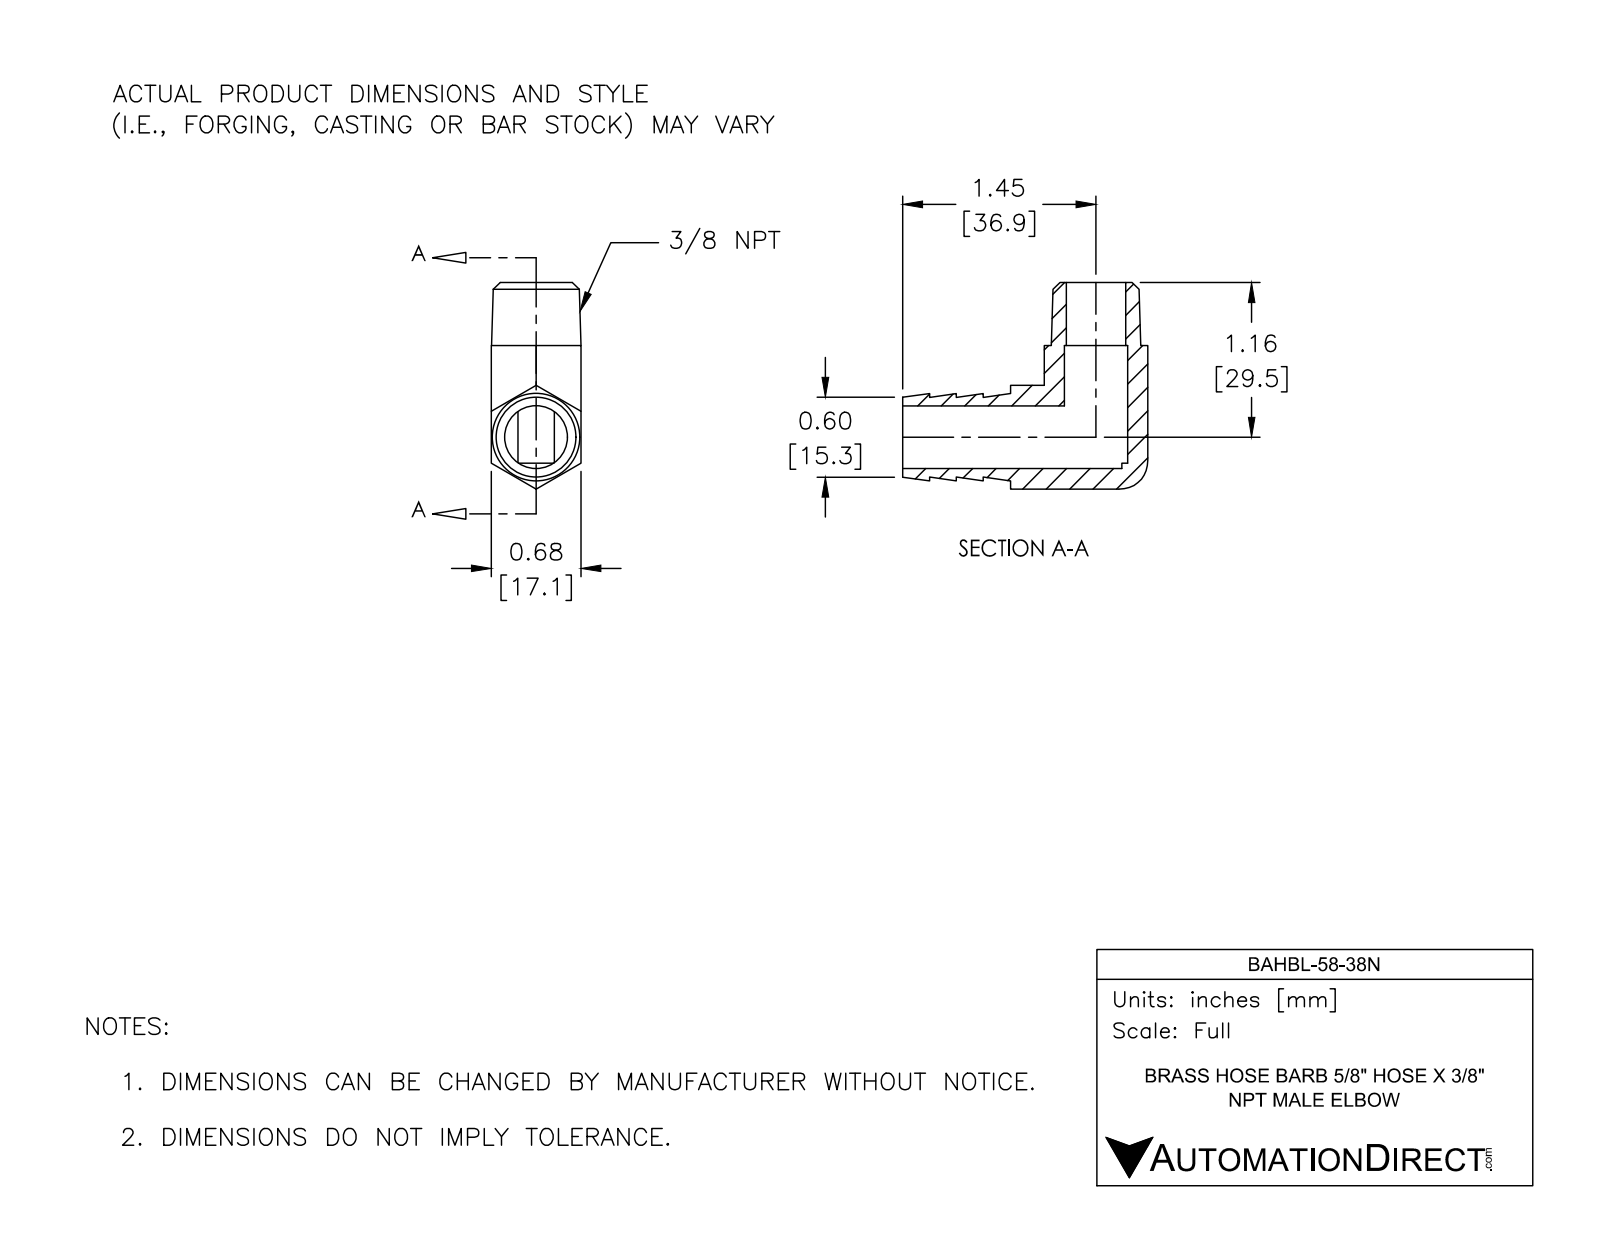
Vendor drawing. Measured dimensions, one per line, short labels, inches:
name: BAHBL-58-38N
written by: SolidWorks 2017 (AUTOMOTIVE_DESIGN)
unit: in
bodies: 1 solid, 47 faces (22 planar, 13 cylindrical, 12 other)
size: 1.844 × 1.553 × 0.675
volume: 0.476 in³; area: 10.08 in²
holes: 1× ⌀0.447, 1× ⌀0.471, 1× ⌀0.476
bosses: 1× ⌀0.657
rounds: 2× R0.25
face distances: 0.675, 0.202, 0.404, 1.358, 1.649, 0.885, 0.473, 1.043, 1.245, 1.447
